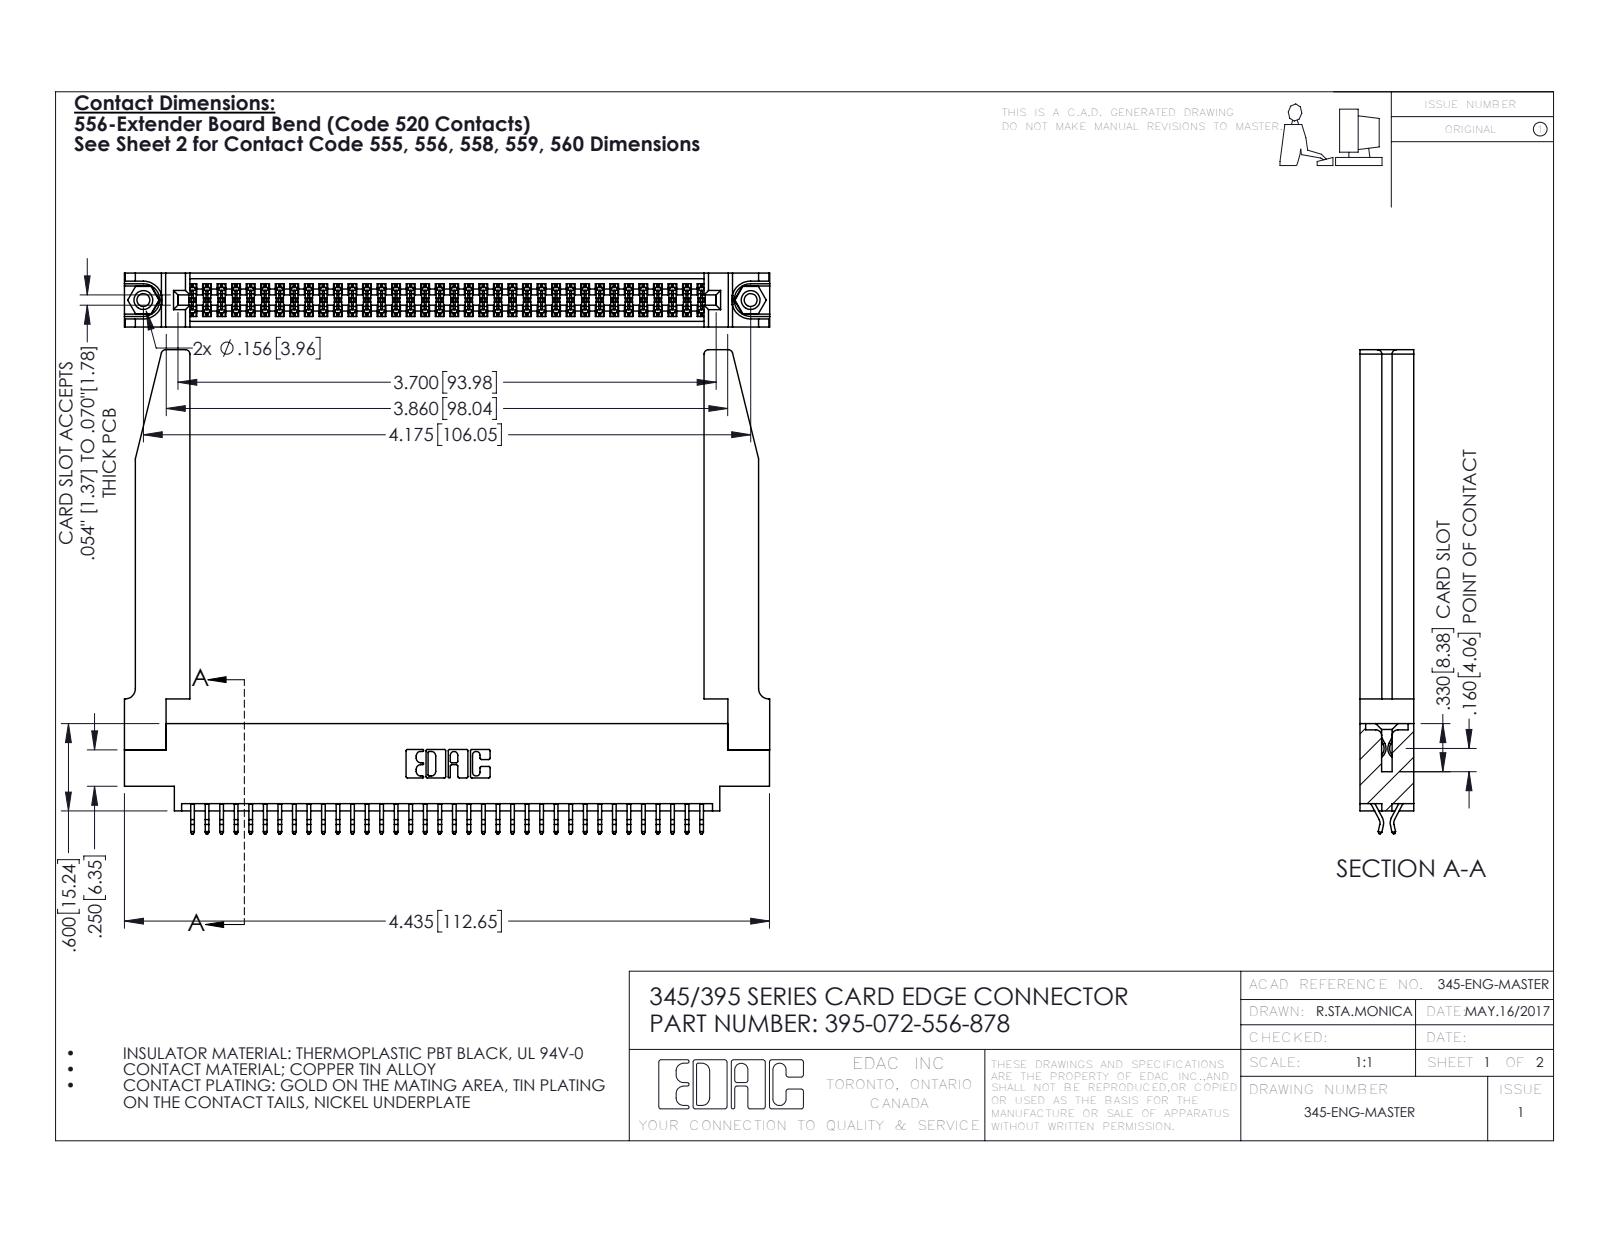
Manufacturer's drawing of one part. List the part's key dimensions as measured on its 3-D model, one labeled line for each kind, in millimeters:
Part name (STEP PRODUCT): 345 Part_0.170 Offset - 0.156 Dia-TH; 345-220-078_345-220-078; 345-292-001_556 Tail; 395-072-556-878 (+1 more)
STEP written by: SolidWorks 2016 (CONFIG_CONTROL_DESIGN)
Units: millimetres
Bodies: 77 solids, 4396 faces (2890 planar, 1454 cylindrical, 52 other)
Overall size (bounding box): 112.7 × 84.5 × 9.4
Volume: 18 550 mm³ · Surface area: 22 730 mm²
Round holes (diameter × count): ⌀2.3 ×2, ⌀3.2 ×2, ⌀4 ×2, ⌀1.6 ×1
Round bosses / shafts (diameter × count): ⌀3.9 ×2
Partial cylindrical surfaces — rounded edges, fillets, slot ends (radius × count): R0.2 ×108, R0.3 ×22, R0.8 ×8, R0.2 ×6, R0.8 ×6, R0.7 ×3, R0.3 ×2, R0.4 ×2
Main face-to-face distances: 9.4, 1.8, 7.6, 0.6, 5.1, 2.5, 6.9, 5.7, 4.4, 3.8
Hole centre spacings: 6.9, 100.1, 106
